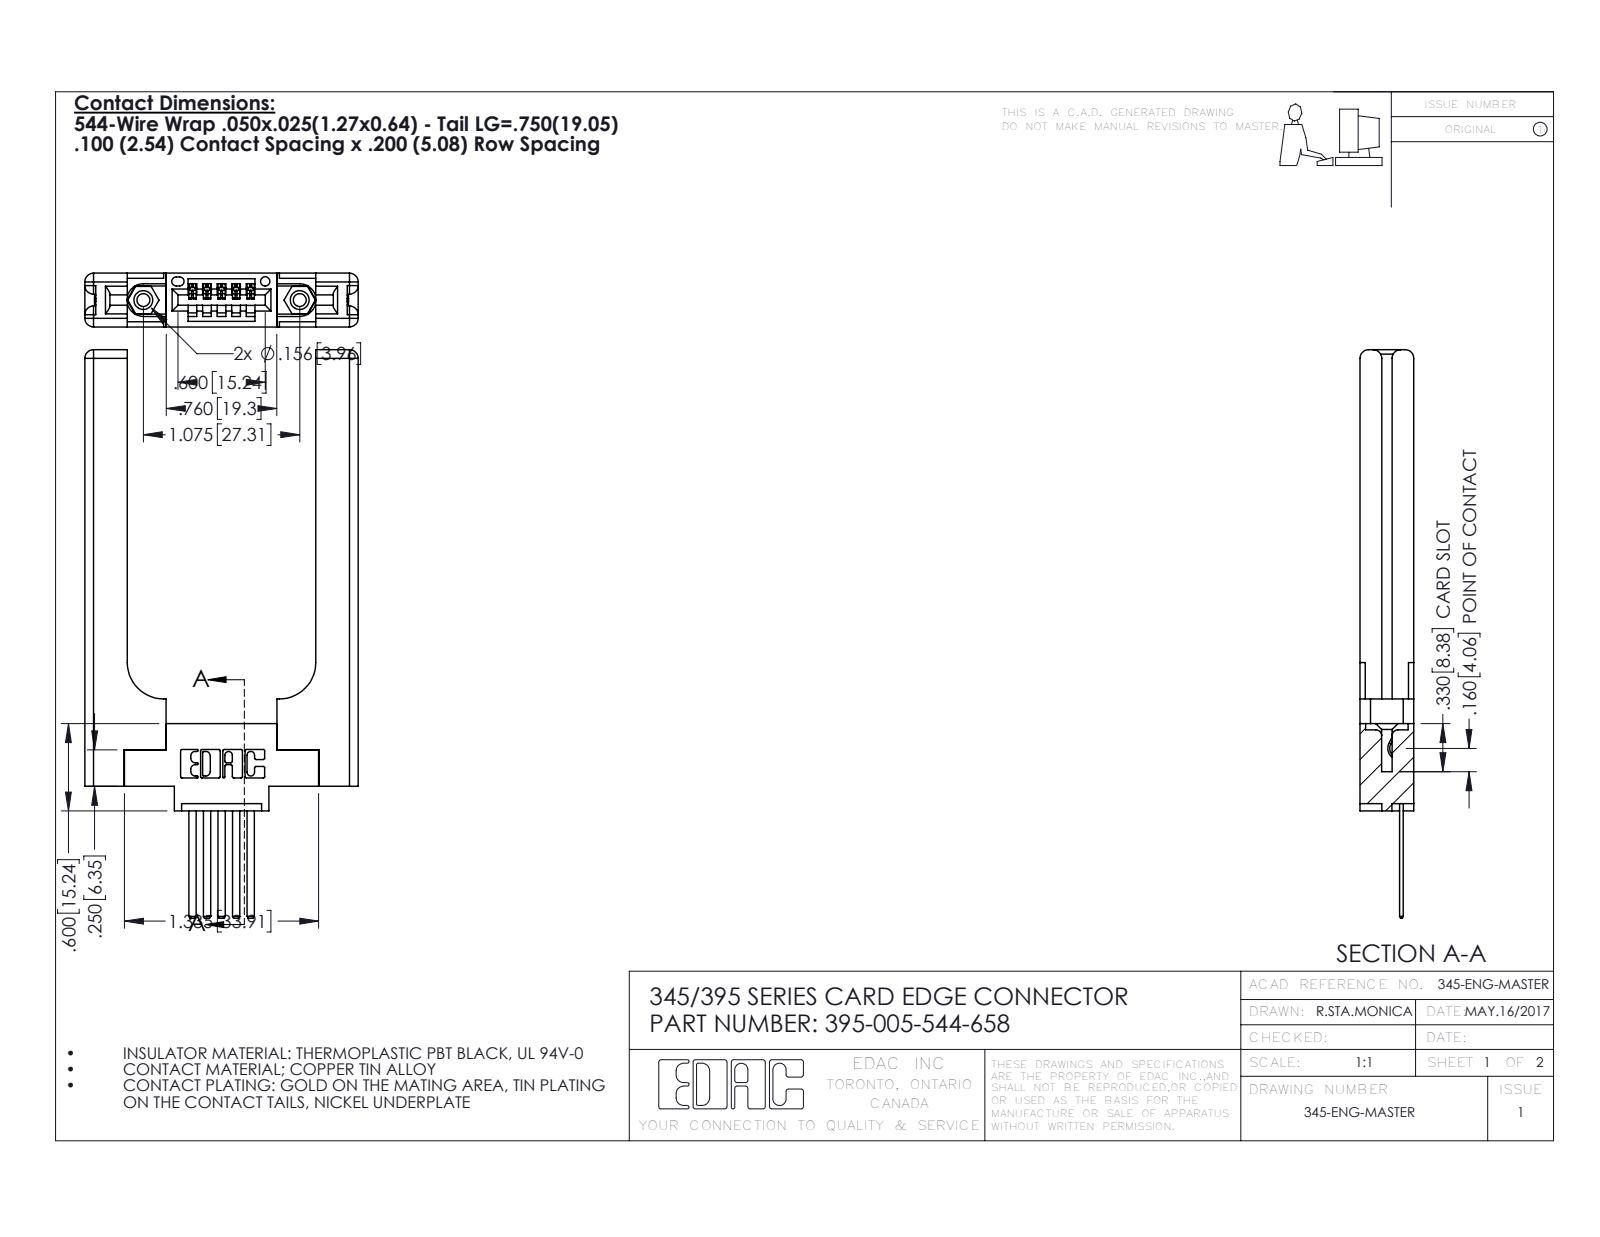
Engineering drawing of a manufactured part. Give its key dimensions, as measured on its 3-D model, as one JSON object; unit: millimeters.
{"part_name": "345-250-001_345-250-001-102; 345-220-058_345-220-058; 345-292-001_345-293-144; 395-005-544-658 (+1 more)", "step_written_by": "SolidWorks 2016 (CONFIG_CONTROL_DESIGN)", "units": "millimeters", "bodies": {"solids": 10, "faces": 646, "planar": 412, "cylindrical": 174, "other": 60}, "overall_size": [99.2, 47.7, 9.4], "volume_mm3": 12700, "surface_area_mm2": 10650, "round_holes": [[2.3, 2], [3.2, 2], [4, 2], [1.6, 1]], "round_bosses_or_shafts": [[3.9, 2]], "partial_cylinders_radius": [[0.3, 22], [1.5, 16], [0.2, 10], [0.2, 6], [0.8, 6], [0.7, 3], [0.8, 2], [0.8, 2]], "face_to_face_distances": [9.4, 3.8, 5.6, 1.8, 3.8, 2, 7.6, 32.9, 1.8, 7.4], "hole_center_spacings": [6.9, 21.5, 27.3]}
